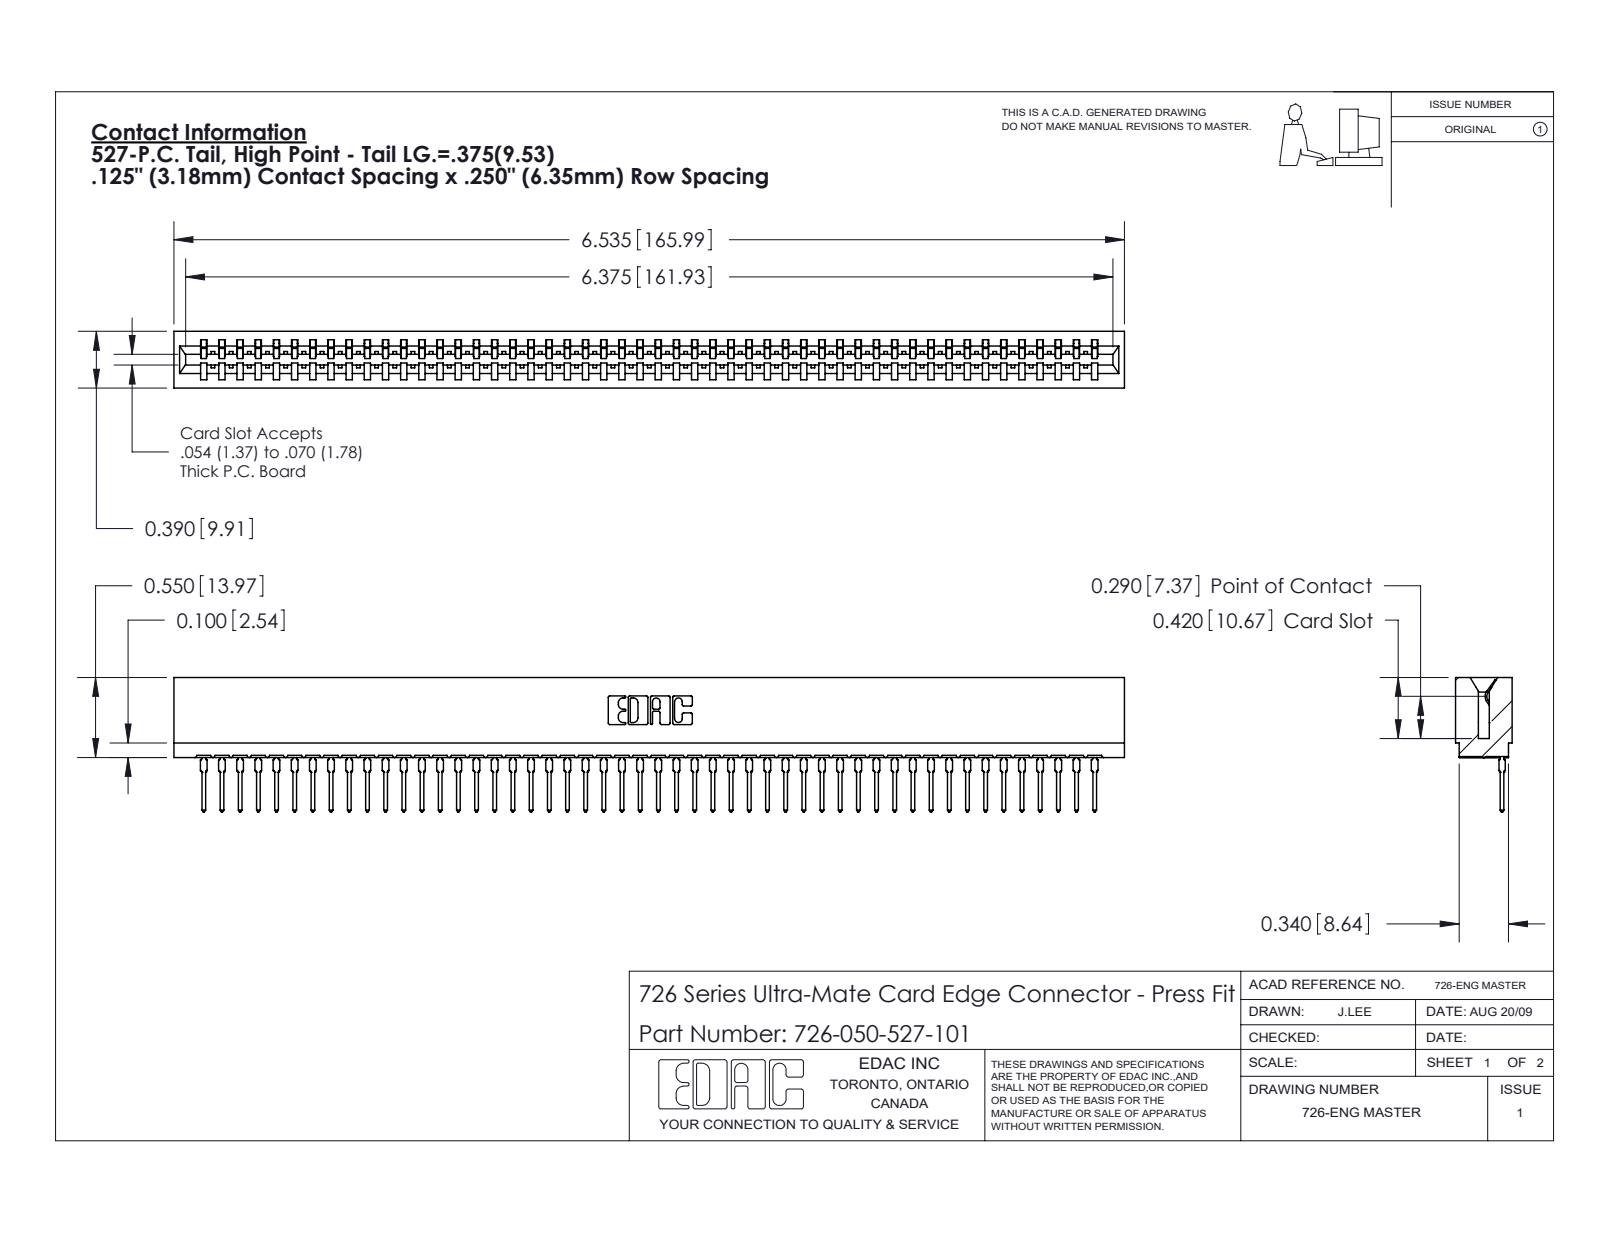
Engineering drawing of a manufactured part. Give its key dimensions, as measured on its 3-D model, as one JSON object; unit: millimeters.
{"part_name": "726-050-527-101; 726 Part_.515 Slot Depth - 01; 746-292-001_527", "step_written_by": "SolidWorks 2020 (CONFIG_CONTROL_DESIGN)", "units": "millimeters", "bodies": {"solids": 51, "faces": 5497, "planar": 3205, "cylindrical": 992, "other": 1300}, "overall_size": [166, 23.5, 9.9], "volume_mm3": 14800, "surface_area_mm2": 23030, "partial_cylinders_radius": [[0.5, 100], [0.4, 51], [0.3, 22], [0.2, 6], [0.8, 6], [0.1, 4], [0.3, 4], [0.7, 3]], "face_to_face_distances": [1.4, 8.5, 9.9, 0.6, 7.8, 6.4, 7, 2.1, 9.3, 0.8]}
